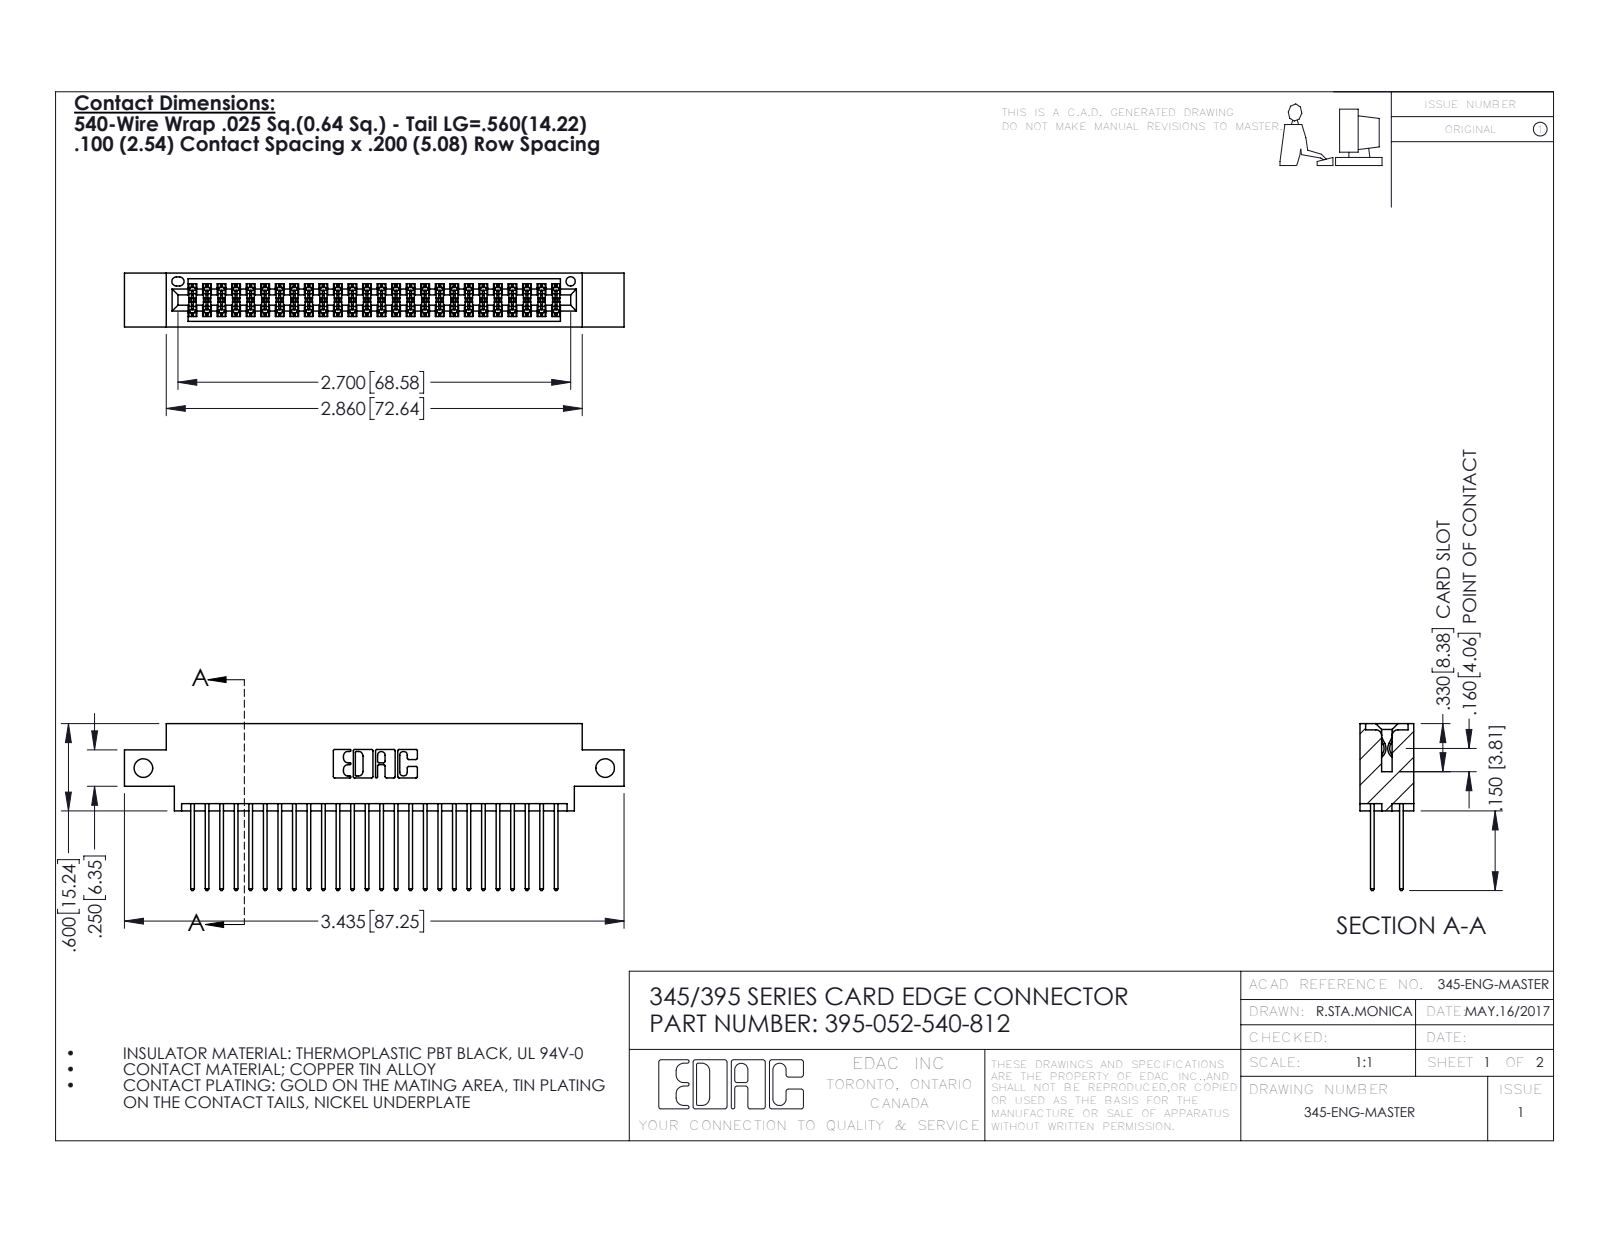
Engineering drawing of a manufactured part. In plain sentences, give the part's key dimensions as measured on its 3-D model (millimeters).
The part is named "345-292-001_345-293-140; 395-052-540-812; 345 Part_0.170 Offset - Side Mount". Its 3-D file was written by "SolidWorks 2016 (CONFIG_CONTROL_DESIGN)". It is 53 solids with 2730 faces: 1800 planar, 930 cylindrical and 0 other. Overall it measures 87.2 by 29.1 by 9.4 millimeters. Its volume is 8 320 cubic millimeters and its surface area 12 920 square millimeters. Round holes: 2 of diameter 3.3, 1 of diameter 1.6. Partial cylindrical surfaces (rounded edges, fillets, slot ends): 78 of radius 0.2, 52 of radius 0.3, 22 of radius 0.3, 6 of radius 0.2, 6 of radius 0.8, 3 of radius 0.7, 2 of radius 0.4, 2 of radius 0.5. The main face-to-face distances are 1.8, 7.6, 5.1, 2.5, 6.9, 0.6, 9.4, 5.7, 4.4, 3.8. The hole center spacings are 80.6.
